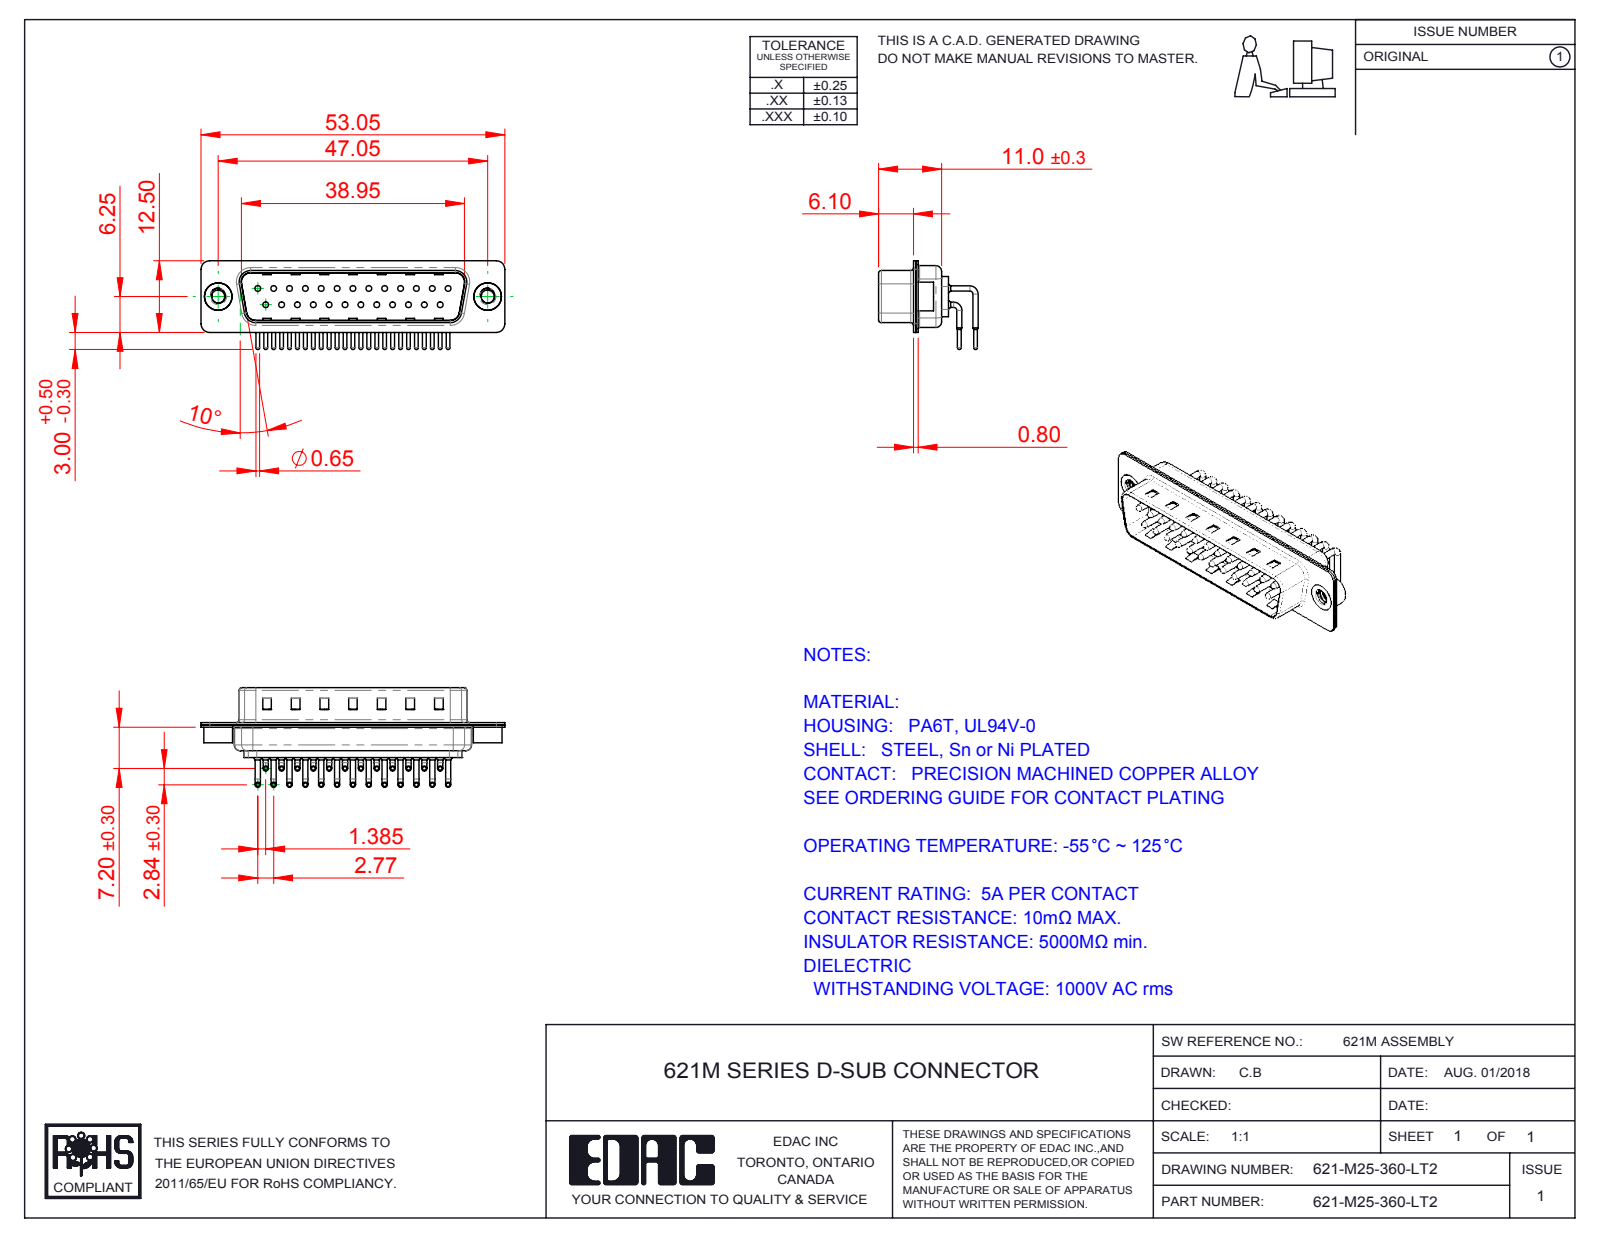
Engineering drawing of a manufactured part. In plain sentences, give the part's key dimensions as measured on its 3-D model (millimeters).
The part is named "621M Housing_25 Contacts; 621-M25-360-LT2; 621M Contact Row 1; 621M Contact Row 2 (+3 more)". Its 3-D file was written by "SolidWorks 2016 (CONFIG_CONTROL_DESIGN)". It is 30 solids with 3126 faces: 1771 planar, 1037 cylindrical and 318 other. Overall it measures 53.05 by 17.39 by 15.49 millimeters. Its volume is 2 875 cubic millimeters and its surface area 7 590 square millimeters. Round holes: 25 of diameter 1, 25 of diameter 1.7, 25 of diameter 2, 2 of diameter 2.26, 2 of diameter 4, 2 of diameter 4.8. Round bosses or shafts: 50 of diameter 0.9, 25 of diameter 1.5, 25 of diameter 0.65, 2 of diameter 5, 2 of diameter 4.9. Partial cylindrical surfaces (rounded edges, fillets, slot ends): 25 of radius 1.01, 16 of radius 1.5, 12 of radius 2, 8 of radius 0.5, 8 of radius 1.6, 4 of radius 0.25, 4 of radius 0.6, 4 of radius 0.65. The main face-to-face distances are 0.4, 0.85, 9.55, 8.7, 1.25, 10.4, 1.5, 1.9, 0.35, 6.1. The hole center spacings are 3.16, 8.31, 2.77, 5.54, 11.08, 16.62, 5.03, 5.04.
